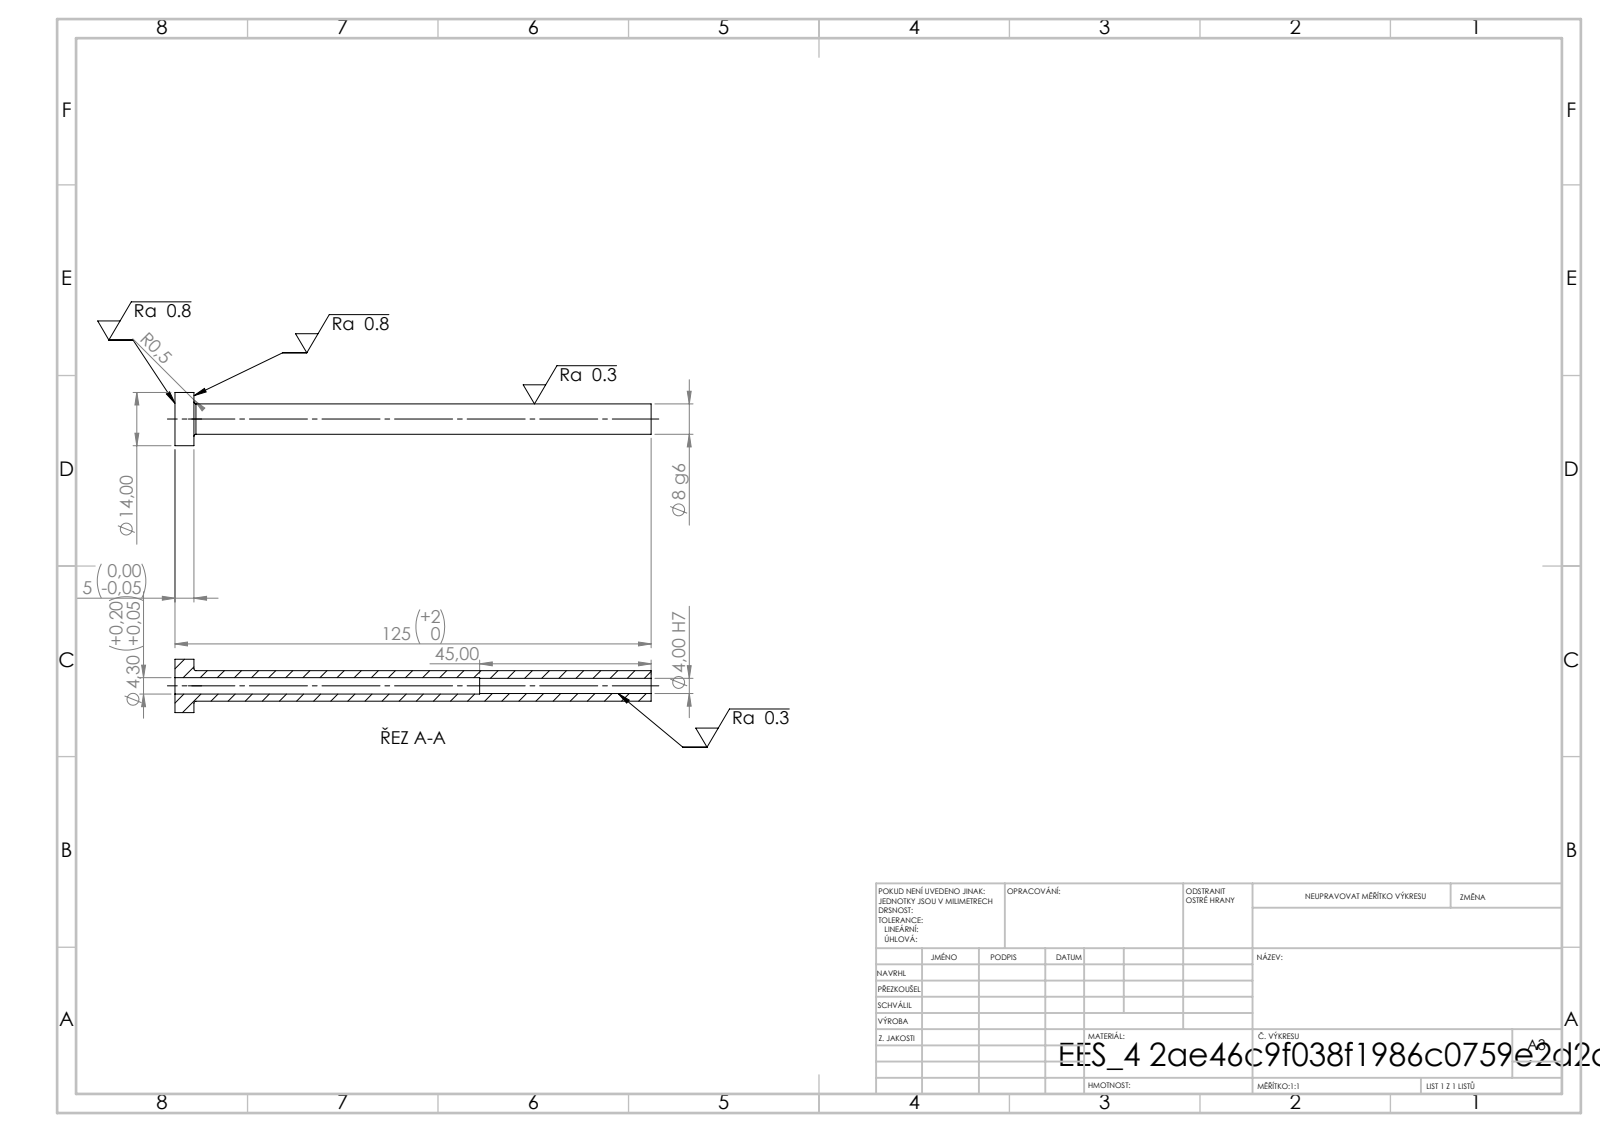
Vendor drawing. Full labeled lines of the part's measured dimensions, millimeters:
STEP written by: SolidWorks 2019 (CONFIG_CONTROL_DESIGN)
Units: millimetres
Bodies: 1 solid, 14 faces (4 planar, 8 cylindrical, 2 other)
Overall size (bounding box): 125 × 14 × 14
Volume: 5 076 mm³ · Surface area: 5 160 mm²
Round holes (diameter × count): ⌀4 ×1, ⌀4.3 ×1
Round bosses / shafts (diameter × count): ⌀14 ×1, ⌀8 ×1
Main face-to-face distances: 5, 125, 120, 80, 75, 45
